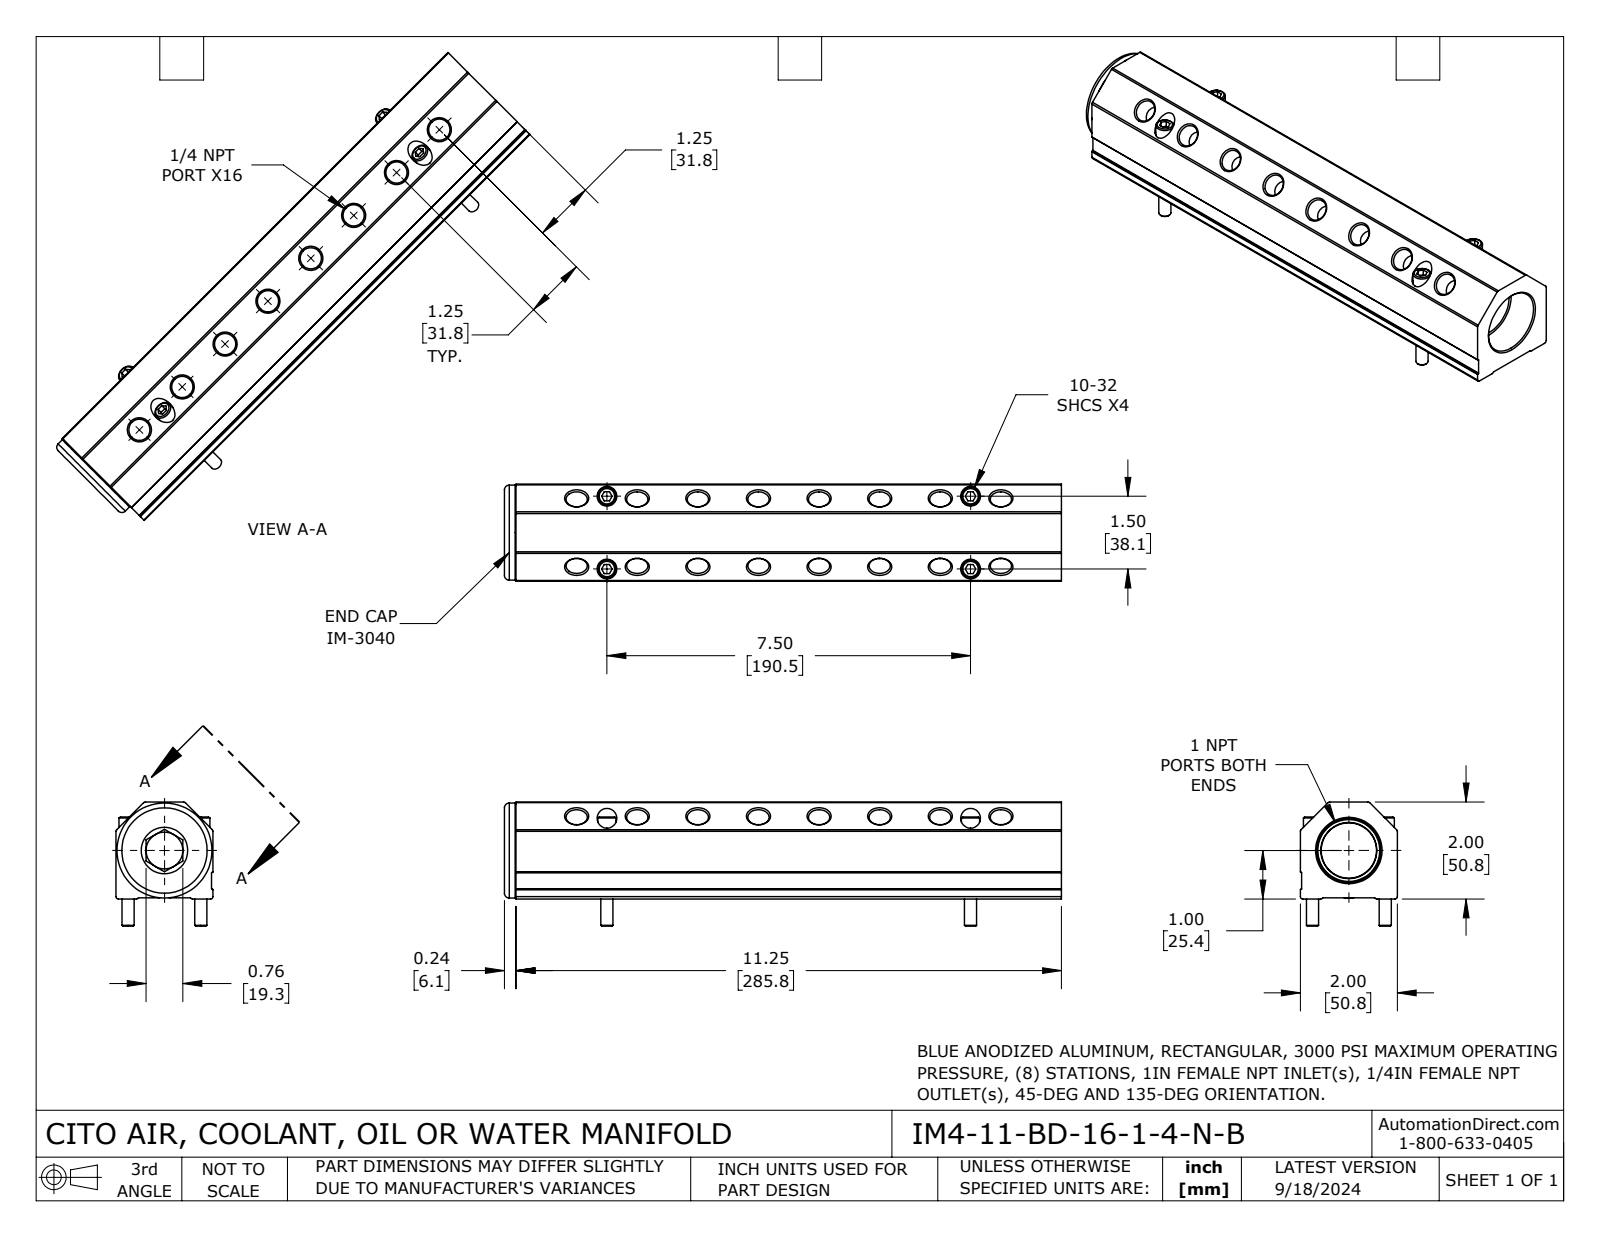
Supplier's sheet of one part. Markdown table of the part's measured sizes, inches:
| quantity | value |
| --- | --- |
| part name | IM4-11-BD-16-1-4-N-B |
| STEP written by | SolidWorks 2023 (CONFIG_CONTROL_DESIGN) |
| units | inches |
| bodies | 6 solids, 245 faces (81 planar, 90 cylindrical, 74 other) |
| overall size | 11.49 × 2.56 × 2 |
| volume | 28.53 in³ |
| surface area | 158.9 in² |
| round holes (diameter × count) | 0.437 × 16, 0.266 × 4, 0.406 × 4, 0.758 × 1, 1.156 × 1, 1.637 × 1 |
| round bosses / shafts (diameter × count) | 0.375 × 4, 0.25 × 4, 1.96 × 1, 1.359 × 1, 1.293 × 1, 1.14 × 1 |
| partial cylindrical surfaces (radius × count) | 0.05 × 8, 0.01 × 4 |
| main face-to-face distances | 2, 1.975, 0.025, 0.028, 1.972, 11.25, 0.24, 11.49, 0.764, 0.524 |
| hole center spacings | 1.25, 2.5, 3.75, 5, 6.25, 7.5, 1.5, 7.648 |
